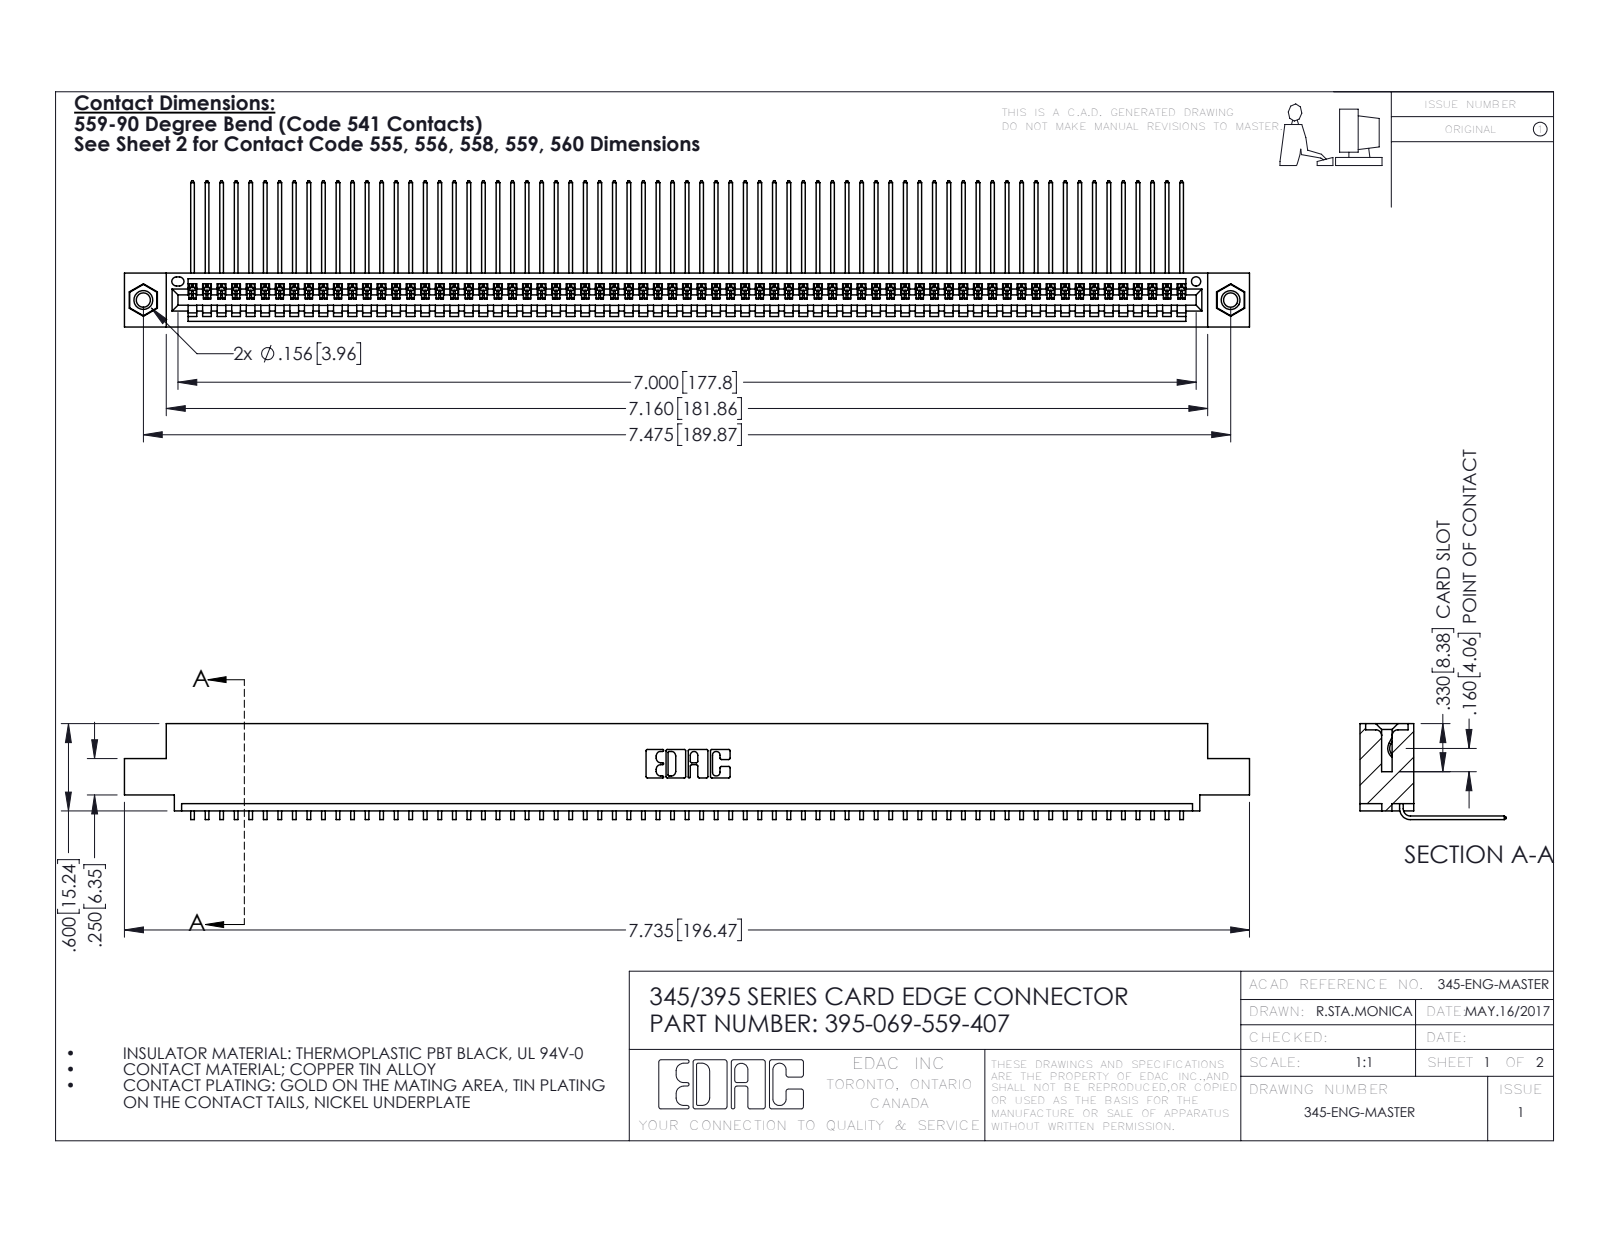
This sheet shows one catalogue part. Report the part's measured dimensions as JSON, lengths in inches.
{"part_name": "345-292-001_558 559 Tail - 1; 395-069-559-407; 345 Part_0.110 Offset - 0.156 Dia-TI; 345-250-001_345-250-005-103", "step_written_by": "SolidWorks 2016 (CONFIG_CONTROL_DESIGN)", "units": "inches", "bodies": {"solids": 72, "faces": 4330, "planar": 3014, "cylindrical": 1300, "other": 16}, "overall_size": [7.735, 1.005, 0.659], "volume_in3": 1.161, "surface_area_in2": 42.03, "round_holes": [[0.098, 2], [0.125, 2], [0.156, 2], [0.064, 1]], "round_bosses_or_shafts": [[0.155, 2]], "partial_cylinders_radius": [[0.006, 138], [0.01, 22], [0.007, 6], [0.031, 6], [0.026, 3], [0.031, 2], [0.04, 2], [0.014, 1]], "face_to_face_distances": [0.072, 0.298, 0.37, 0.2, 0.098, 0.272, 0.025, 0.225, 0.149, 0.072], "hole_center_spacings": [0.27, 7.239, 7.475]}
